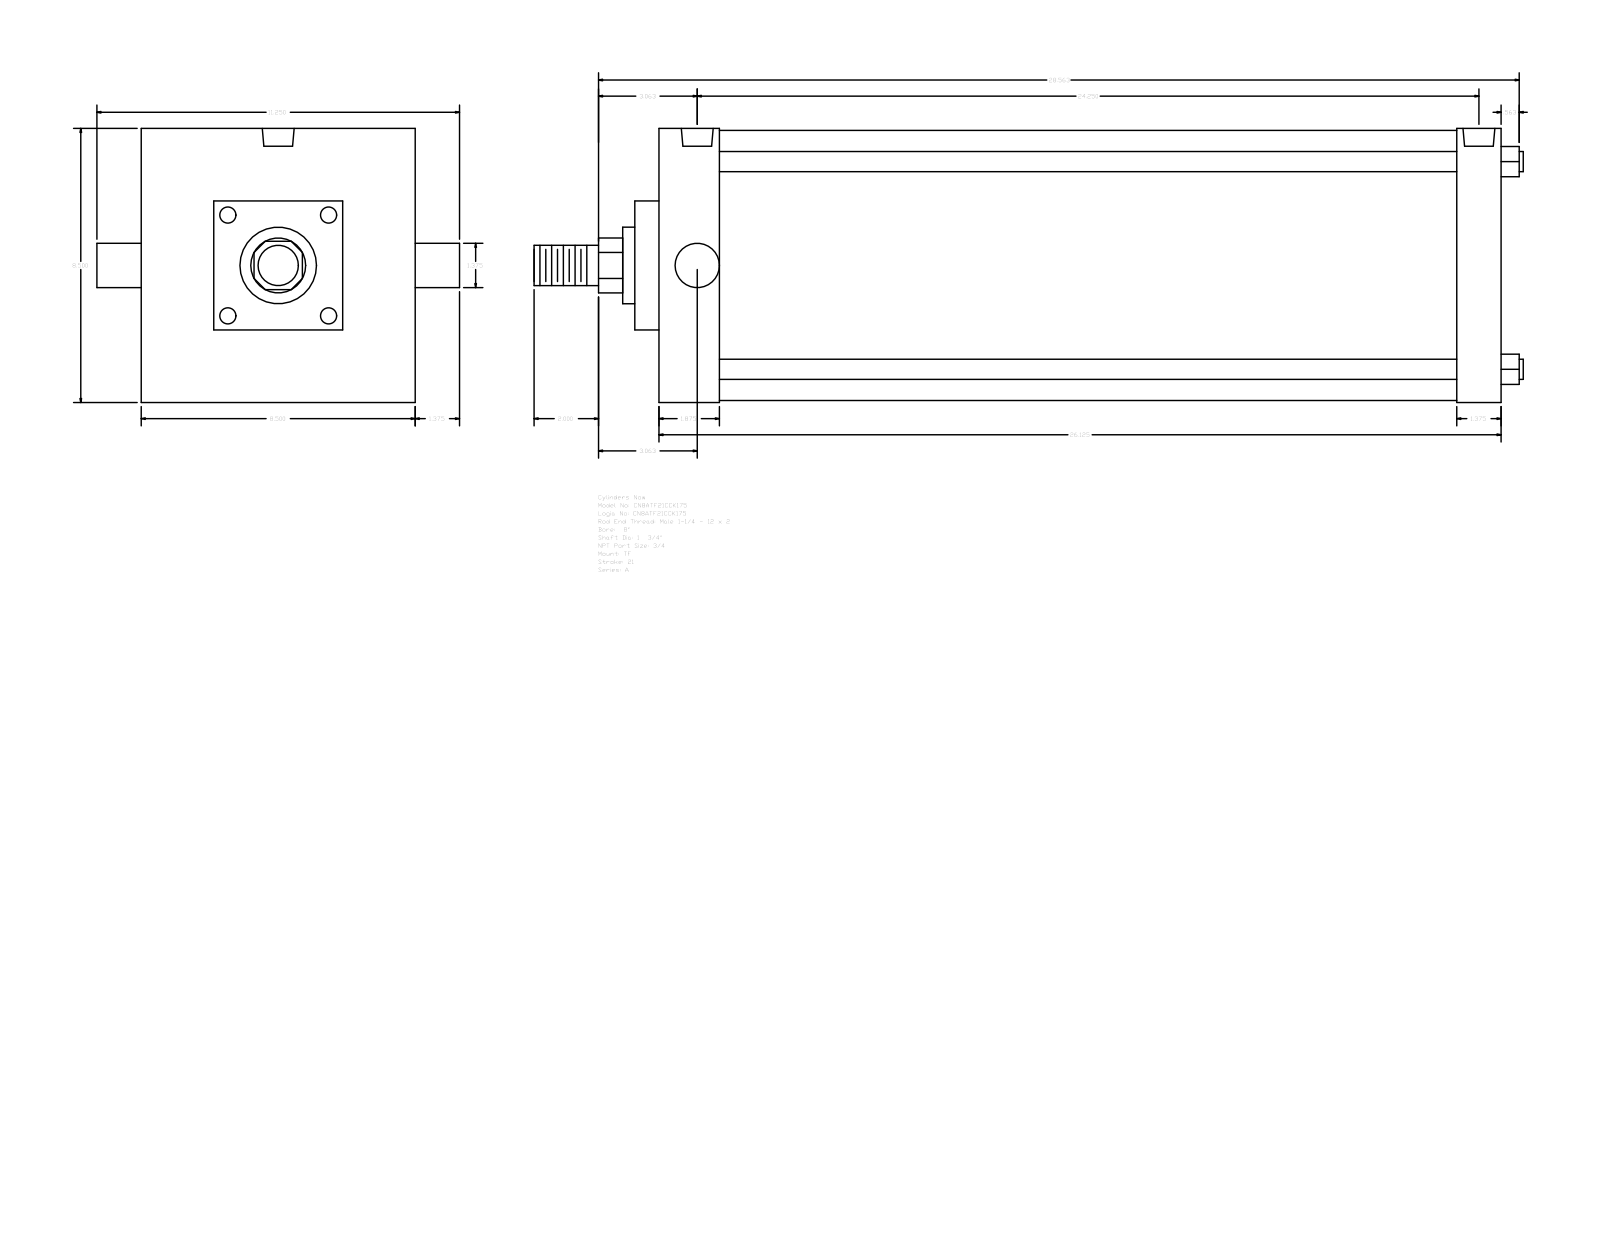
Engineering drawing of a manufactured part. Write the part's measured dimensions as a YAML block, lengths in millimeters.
part_name: "A_TF__0800_1.75"
step_written_by: "GSSL Pune (CONFIG_CONTROL_DESIGN)"
units: millimeters
bodies: {solids: 0, faces: 89, planar: 65, cylindrical: 24, other: 0}
overall_size: [779.46, 285.75, 215.9]
round_holes:
  - {diameter: 15.08, count: 3}
  - {diameter: 25.12, count: 2}
round_bosses_or_shafts:
  - {diameter: 15.88, count: 4}
  - {diameter: 212.72, count: 1}
  - {diameter: 60.33, count: 1}
  - {diameter: 44.45, count: 1}
  - {diameter: 34.92, count: 1}
  - {diameter: 31.75, count: 1}
partial_cylinders:
  - {radius: 21.63, count: 1}
face_to_face_distances: [663.58, 215.9, 34.93, 47.63, 615.95, 628.65, 581.02, 19.05, 57.15, 158.75]
hole_center_spacings: [6.35, 609.6, 603.25, 615.95]
